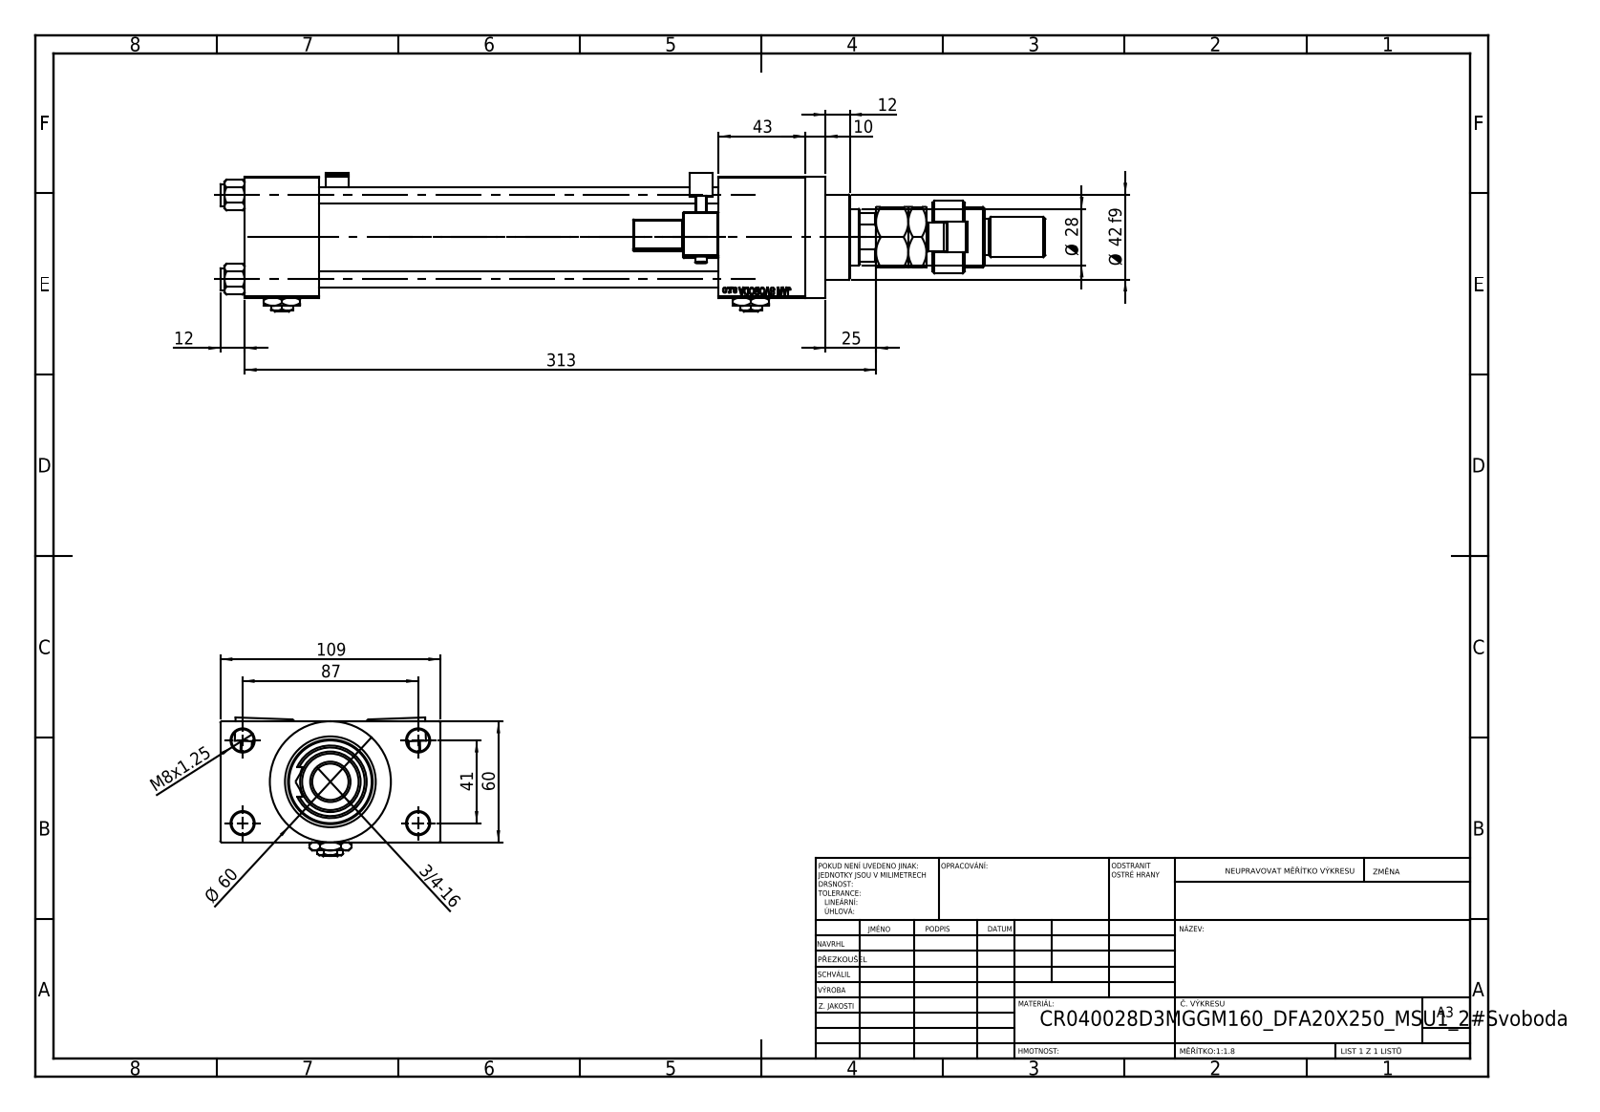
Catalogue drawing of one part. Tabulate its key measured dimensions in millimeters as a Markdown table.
| quantity | value |
| --- | --- |
| part name | V215_VC_A; V215CR_MSU; MFA; NUT_M5_D (+5 more) |
| STEP written by | SolidWorks 2019 (CONFIG_CONTROL_DESIGN) |
| units | millimeters |
| bodies | 17 solids, 1445 faces (632 planar, 173 cylindrical, 640 other) |
| overall size | 409 × 109 × 68.9 |
| volume | 792 792 mm³ |
| surface area | 220 019 mm² |
| round holes (diameter × count) | 8 × 4, 11 × 4, 7 × 2, 16.66 × 2, 24 × 2, 18.5 × 1, 28 × 1, 31 × 1, 40 × 1, 45 × 1 |
| round bosses / shafts (diameter × count) | 11 × 4, 6 × 2, 60 × 1, 46 × 1, 42 × 1, 36 × 1, 30 × 1, 22 × 1 |
| partial cylindrical surfaces (radius × count) | 0.5 × 48, 1 × 2, 2.5 × 2, 4 × 2, 7.5 × 1, 12 × 1, 13.5 × 1 |
| main face-to-face distances | 60, 198, 24.5, 84.5, 37, 235, 43, 278, 241, 109 |
| hole center spacings | 22.65, 29.49, 41.7, 47.15, 48.09, 64.35, 76.49, 41 |
